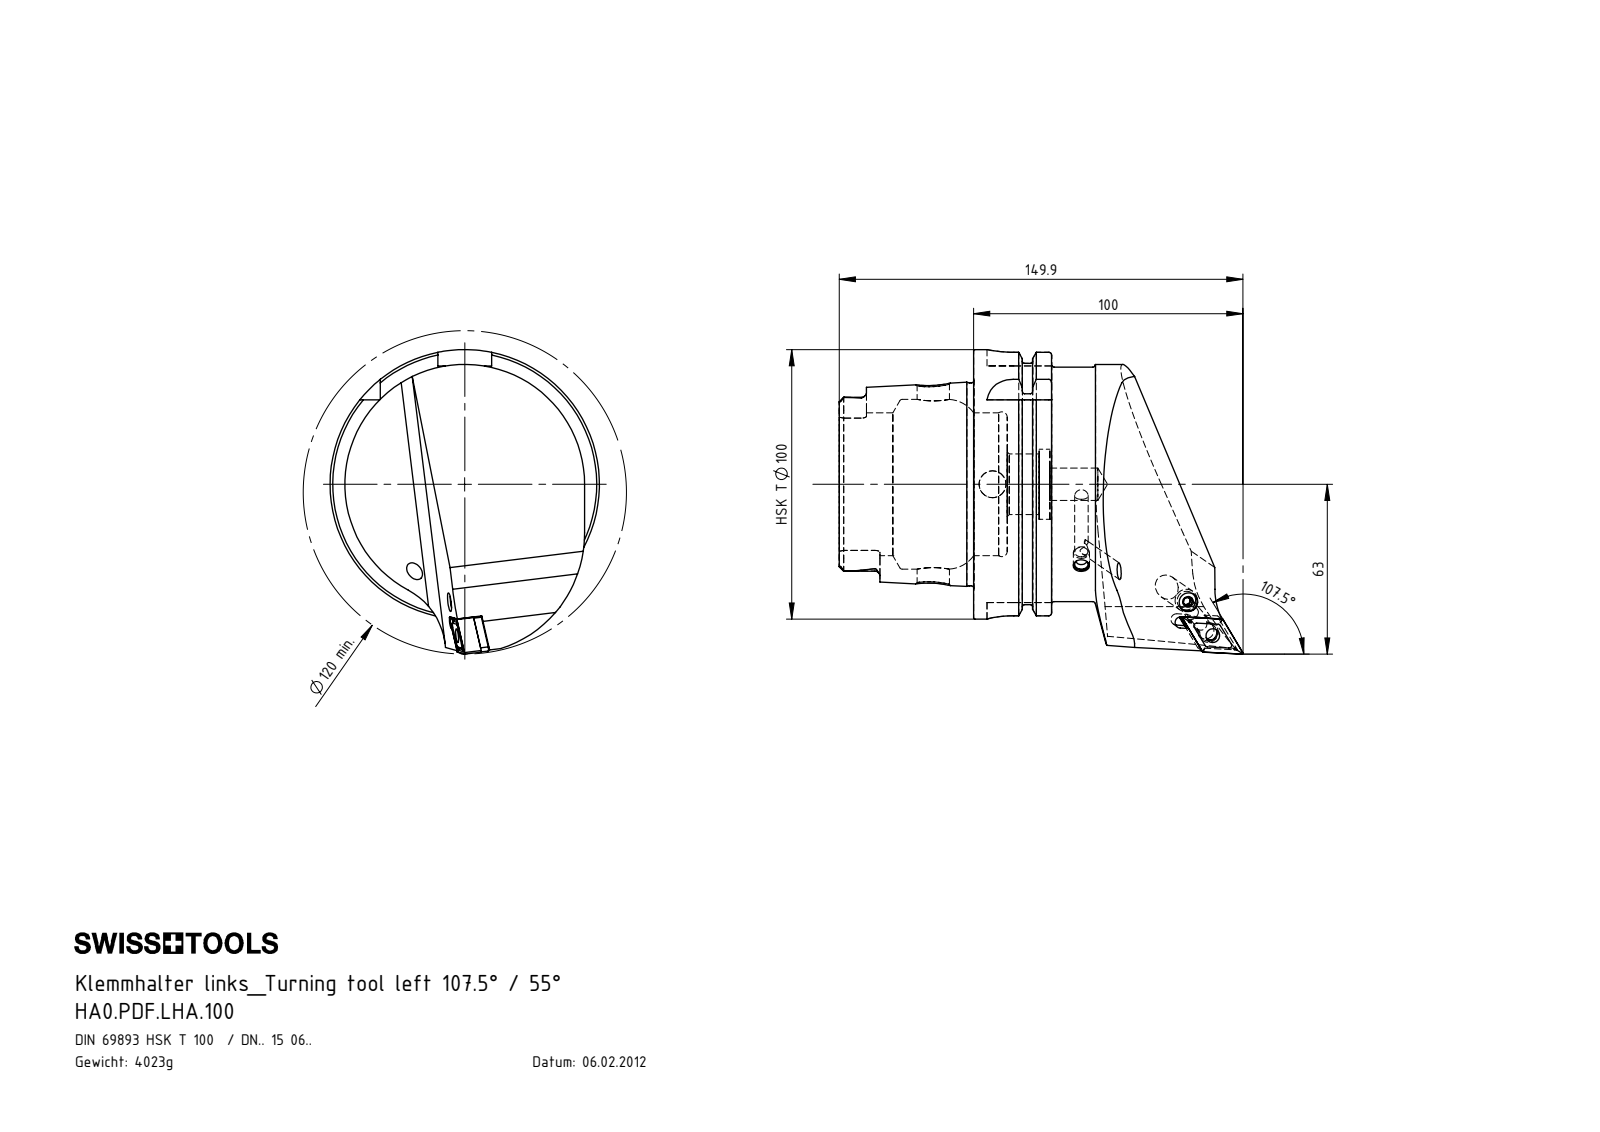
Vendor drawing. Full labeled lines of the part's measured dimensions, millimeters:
Part name (STEP PRODUCT): WDF-ER3.101.000_A; WCD-ER4.101.017_A; WDF-ER2.101.003_A; WCD-ER1.101.000 (+4 more)
STEP written by: SolidWorks 2012 (AUTOMOTIVE_DESIGN)
Units: millimetres
Bodies: 8 solids, 376 faces (115 planar, 106 cylindrical, 155 other)
Overall size (bounding box): 149.9 × 113.01 × 100
Volume: 513 460 mm³ · Surface area: 70 133 mm²
Round holes (diameter × count): ⌀5 ×3, ⌀12 ×2, ⌀5.16 ×1, ⌀6 ×1, ⌀6.4 ×1, ⌀7 ×1, ⌀8.4 ×1, ⌀10 ×1, ⌀22.5 ×1, ⌀26 ×1, ⌀53 ×1, ⌀63 ×1
Round bosses / shafts (diameter × count): ⌀100 ×1, ⌀91.95 ×1, ⌀87 ×1, ⌀75.26 ×1, ⌀8 ×1, ⌀7.9 ×1, ⌀6.4 ×1, ⌀6 ×1
Partial cylindrical surfaces — rounded edges, fillets, slot ends (radius × count): R1.9 ×6, R0.4 ×4, R1 ×4, R10 ×4, R2.5 ×2, R4.83 ×2, R4.88 ×2, R26 ×2
Main face-to-face distances: 12.45, 28.95, 16.5, 49.9, 62.35, 78.85, 87.8, 78.2, 28.3, 15.85
Hole centre spacings: 15.57
